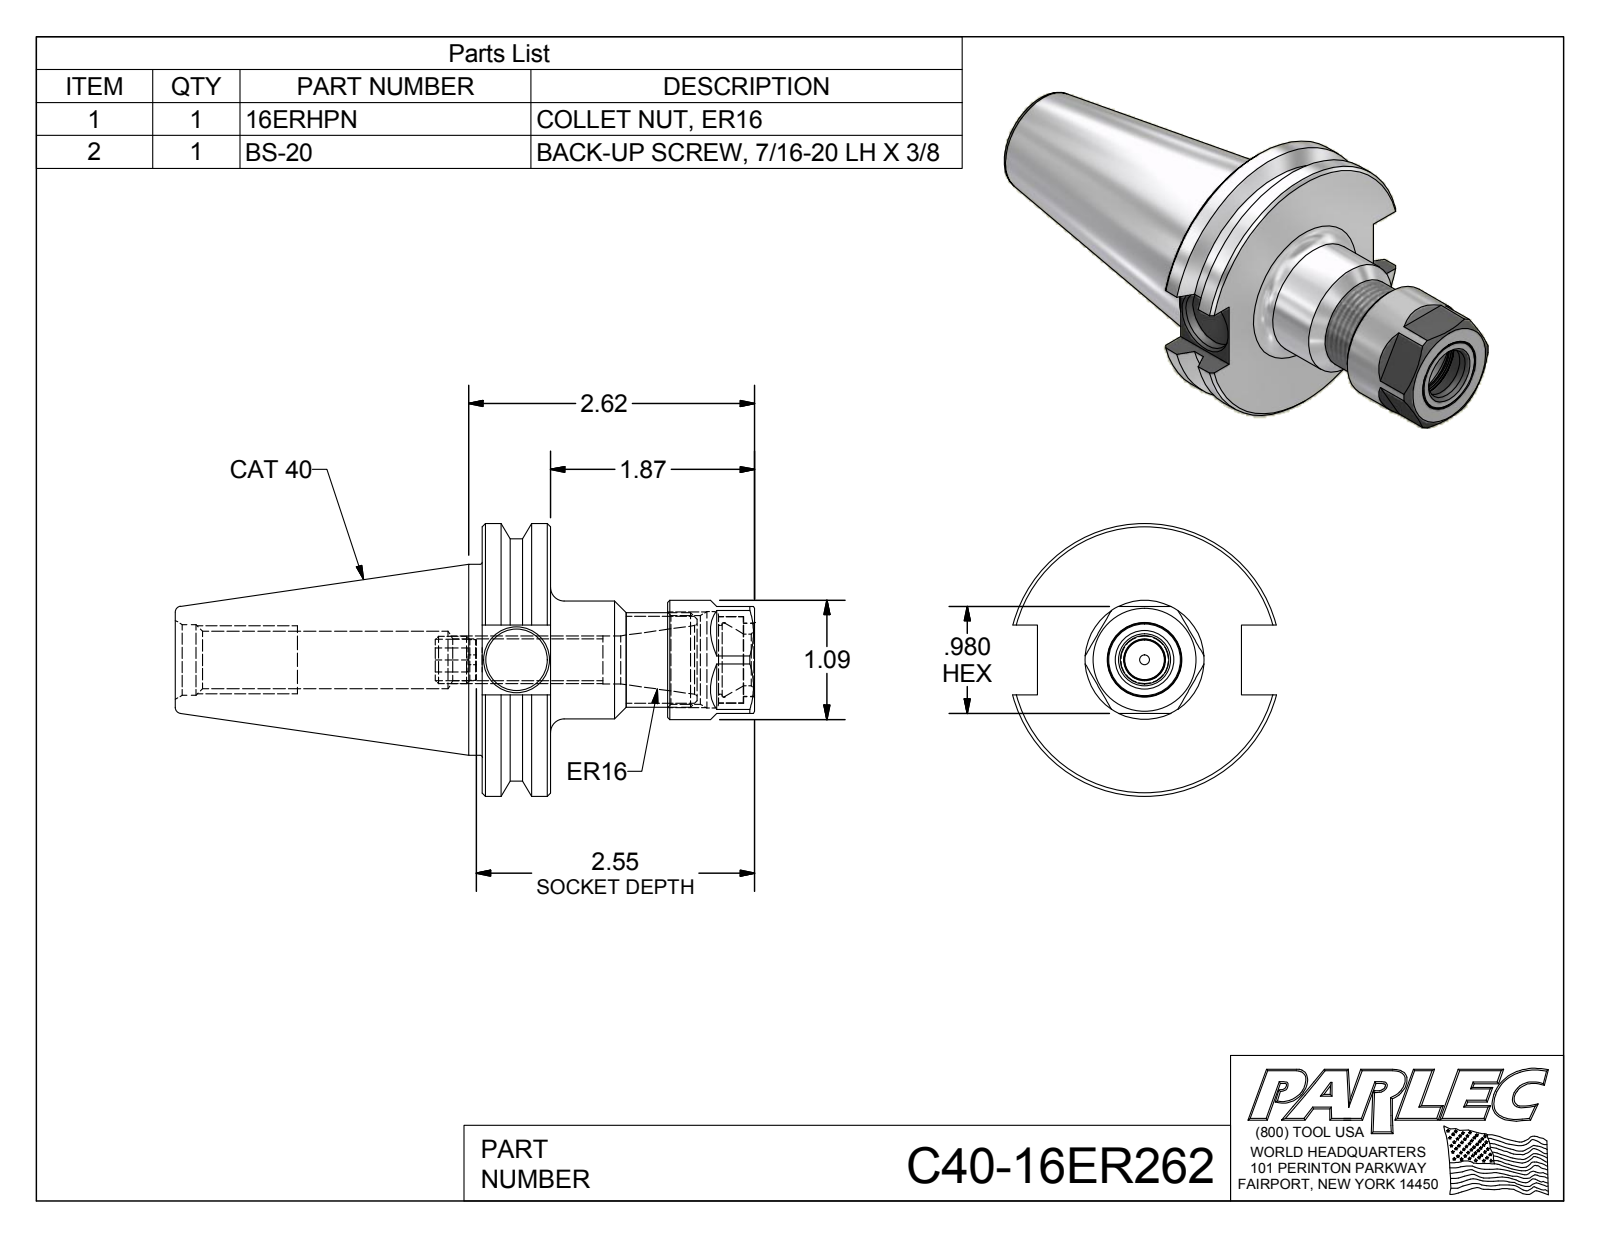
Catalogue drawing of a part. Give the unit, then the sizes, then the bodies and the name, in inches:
Units: inches
Overall size (bounding box): 5.309 × 2.5 × 2.417
Round holes (diameter × count): ⌀0.09 ×1, ⌀0.383 ×1, ⌀0.44 ×1, ⌀0.474 ×1, ⌀0.527 ×1, ⌀0.563 ×1, ⌀0.63 ×1, ⌀0.648 ×1, ⌀0.674 ×1, ⌀0.68 ×1, ⌀0.794 ×1, ⌀0.814 ×1
Round bosses / shafts (diameter × count): ⌀2.5 ×1, ⌀2.219 ×1, ⌀1.75 ×1, ⌀1.092 ×1, ⌀1.08 ×1, ⌀0.866 ×1, ⌀0.79 ×1, ⌀0.67 ×1
Main face-to-face distances: 0.625, 0.98, 2.497, 1.872, 0.17, 0.81, 0.64, 1.701, 1.076, 0.796
Volume: 7.399 in³ · Surface area: 44.8 in²
Bodies: 4 solids, 104 faces (40 planar, 27 cylindrical, 37 other)
Part name (STEP PRODUCT): C40-16ER262; C40-16ER2-1; 16ERHPN; BS-20
STEP written by: Autodesk Inventor 2012 (AUTOMOTIVE_DESIGN)
